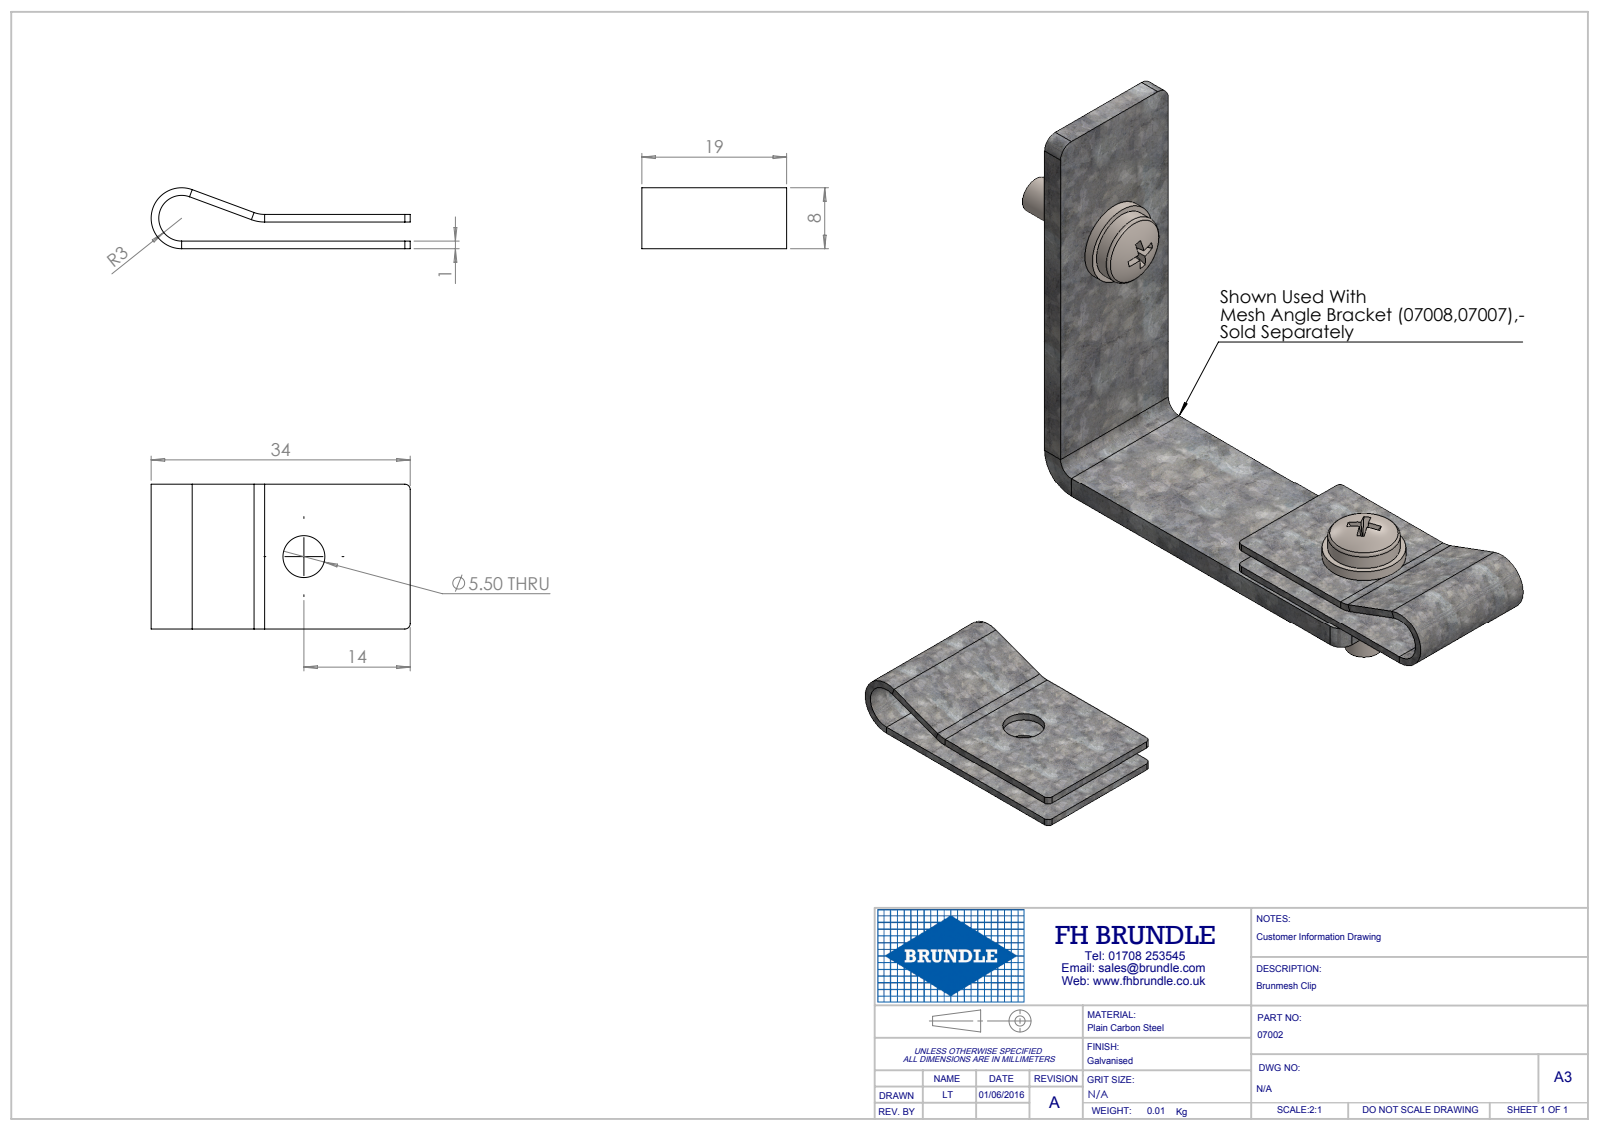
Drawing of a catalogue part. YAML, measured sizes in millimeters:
part_name: "07002"
step_written_by: "SolidWorks 2023 (CONFIG_CONTROL_DESIGN)"
units: millimeters
bodies: {solids: 1, faces: 32, planar: 18, cylindrical: 14, other: 0}
overall_size: [34, 19, 8]
volume: 1312
surface_area: 2839
round_holes:
  - {diameter: 5.5, count: 1}
partial_cylinders:
  - {radius: 0.7, count: 2}
  - {radius: 4, count: 2}
  - {radius: 3, count: 1}
  - {radius: 5, count: 1}
face_to_face_distances: [1, 3.5, 4.5, 2.5, 19]
